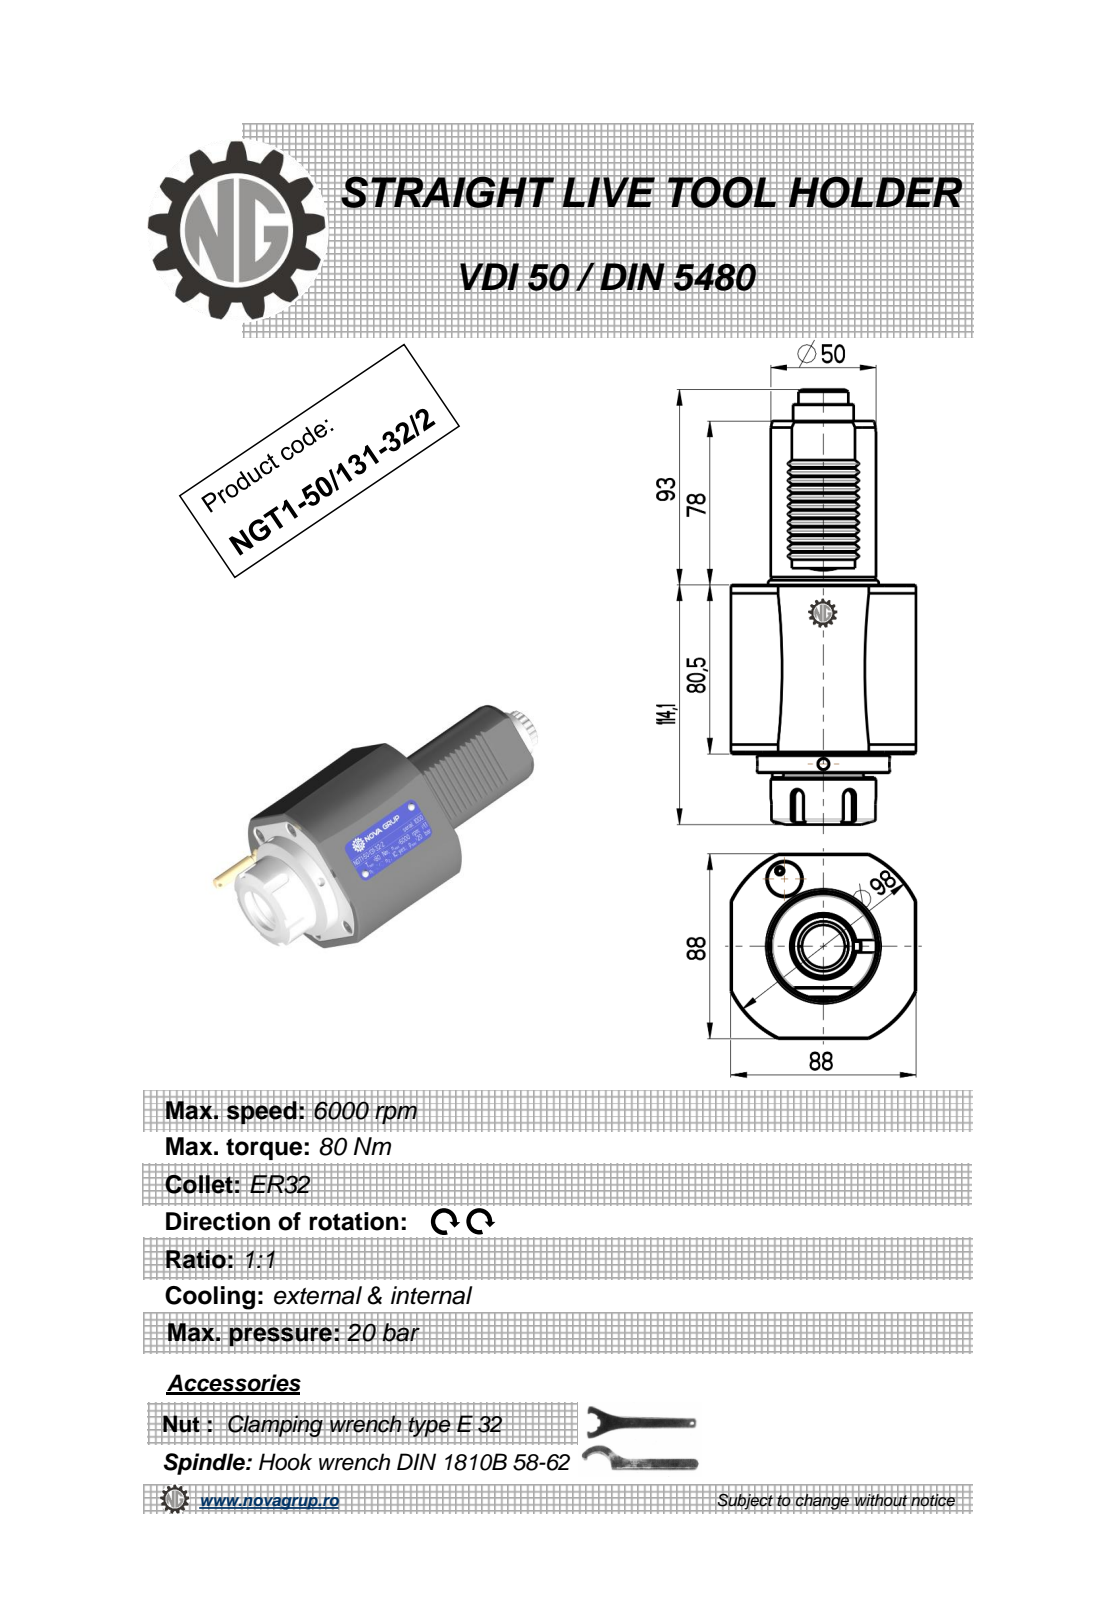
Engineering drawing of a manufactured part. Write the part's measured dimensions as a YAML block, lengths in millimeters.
part_name: "NGT1_50_131_32_1"
step_written_by: "PRO/ENGINEER BY PARAMETRIC TECHNOLOGY CORPORATION, 2010280 (CONFIG_CONTROL_DESIGN)"
units: millimeters
bodies: {solids: 1, faces: 365, planar: 111, cylindrical: 130, other: 124}
overall_size: [207.1, 88, 88]
volume: 777362
surface_area: 63145
round_holes:
  - {diameter: 5, count: 2}
  - {diameter: 2.5, count: 1}
  - {diameter: 3, count: 1}
  - {diameter: 27, count: 1}
round_bosses_or_shafts:
  - {diameter: 63, count: 1}
  - {diameter: 51.1, count: 1}
  - {diameter: 50, count: 1}
  - {diameter: 41, count: 1}
  - {diameter: 28.8, count: 1}
  - {diameter: 9, count: 1}
  - {diameter: 7, count: 1}
  - {diameter: 5, count: 1}
partial_cylinders:
  - {radius: 3.04, count: 36}
  - {radius: 0.3, count: 12}
  - {radius: 3, count: 5}
  - {radius: 10.56, count: 1}
  - {radius: 11.88, count: 1}
  - {radius: 17.5, count: 1}
  - {radius: 49, count: 1}
face_to_face_distances: [88, 80.5, 9, 89.5, 2.83, 78, 81, 0.5, 8.5, 158.5]
hole_center_spacings: [41.5]
